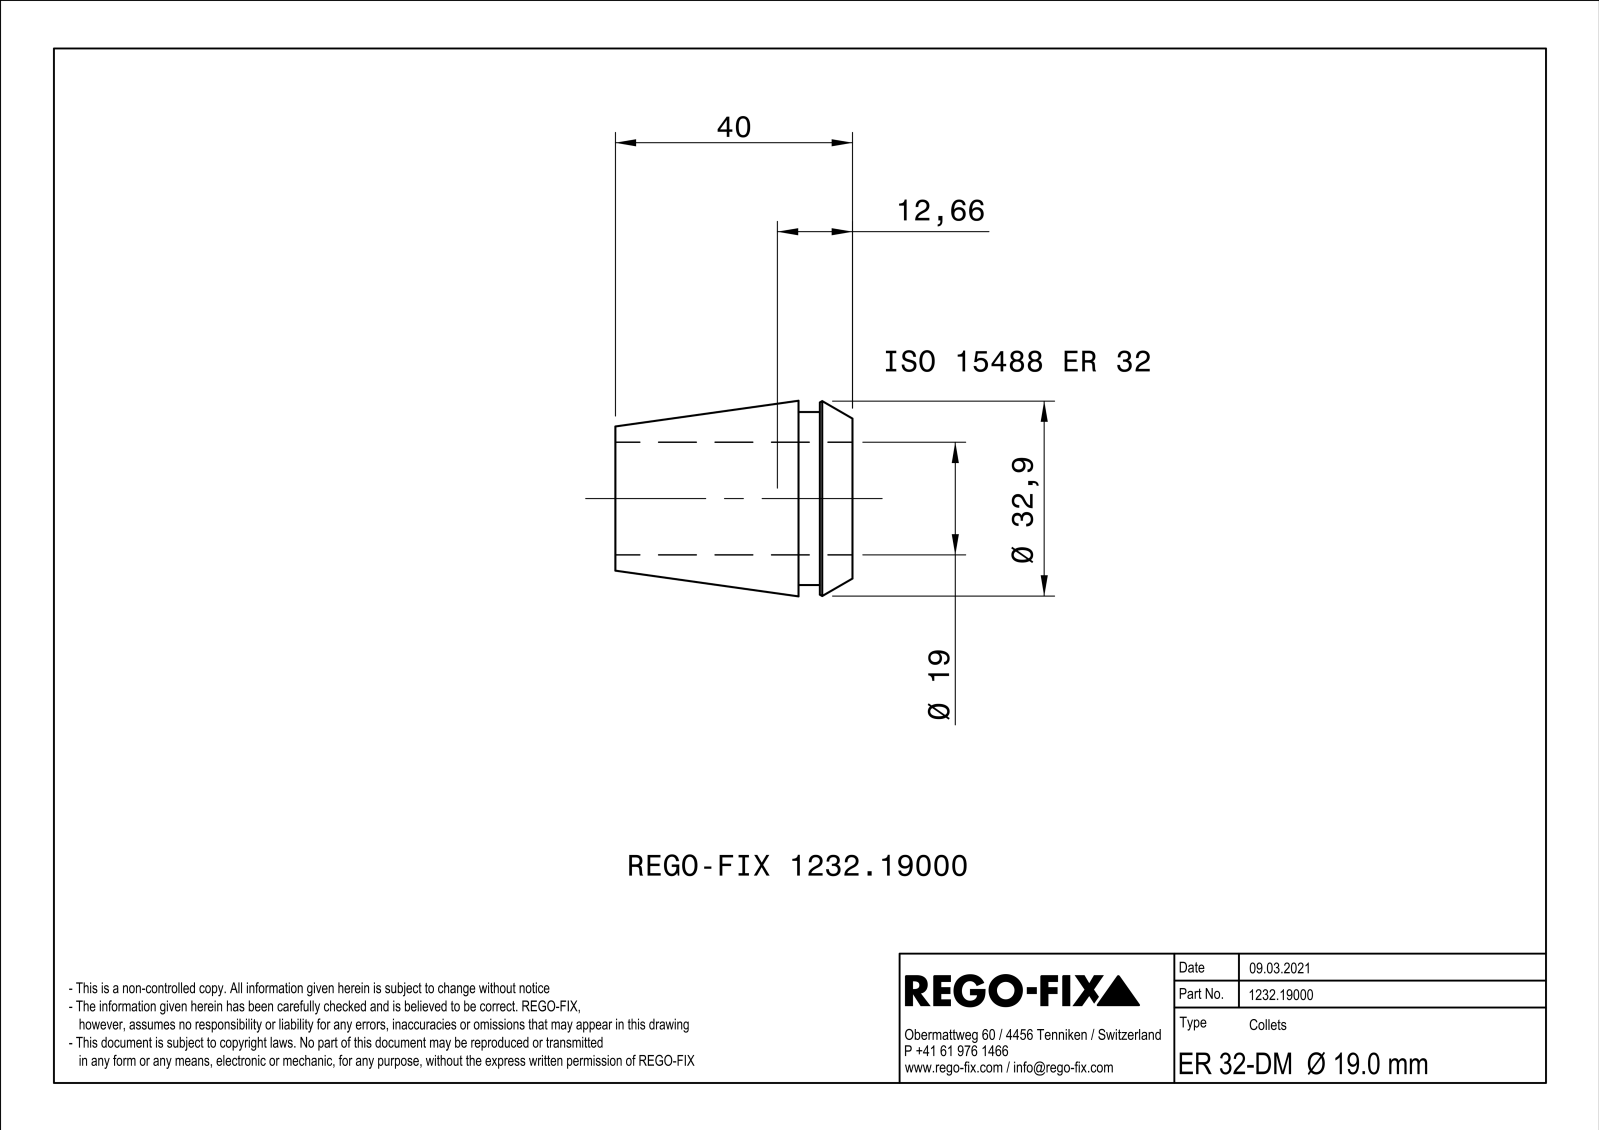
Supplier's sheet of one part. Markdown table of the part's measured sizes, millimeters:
| quantity | value |
| --- | --- |
| part name | NOCUT |
| STEP written by | SIEMENS PLM Software Solid Edge ST10 (AUTOMOTIVE_DESIGN) |
| units | millimeters |
| bodies | 1 solid, 154 faces (80 planar, 9 cylindrical, 65 other) |
| overall size | 40 × 32.98 × 32.98 |
| volume | 12 788 mm³ |
| surface area | 10 550 mm² |
| round holes (diameter × count) | 19 × 1 |
| round bosses / shafts (diameter × count) | 29.2 × 1 |
| main face-to-face distances | 1, 9.1, 40, 30.9, 5.5, 3.6, 34.5, 16, 10.5, 6.9 |
